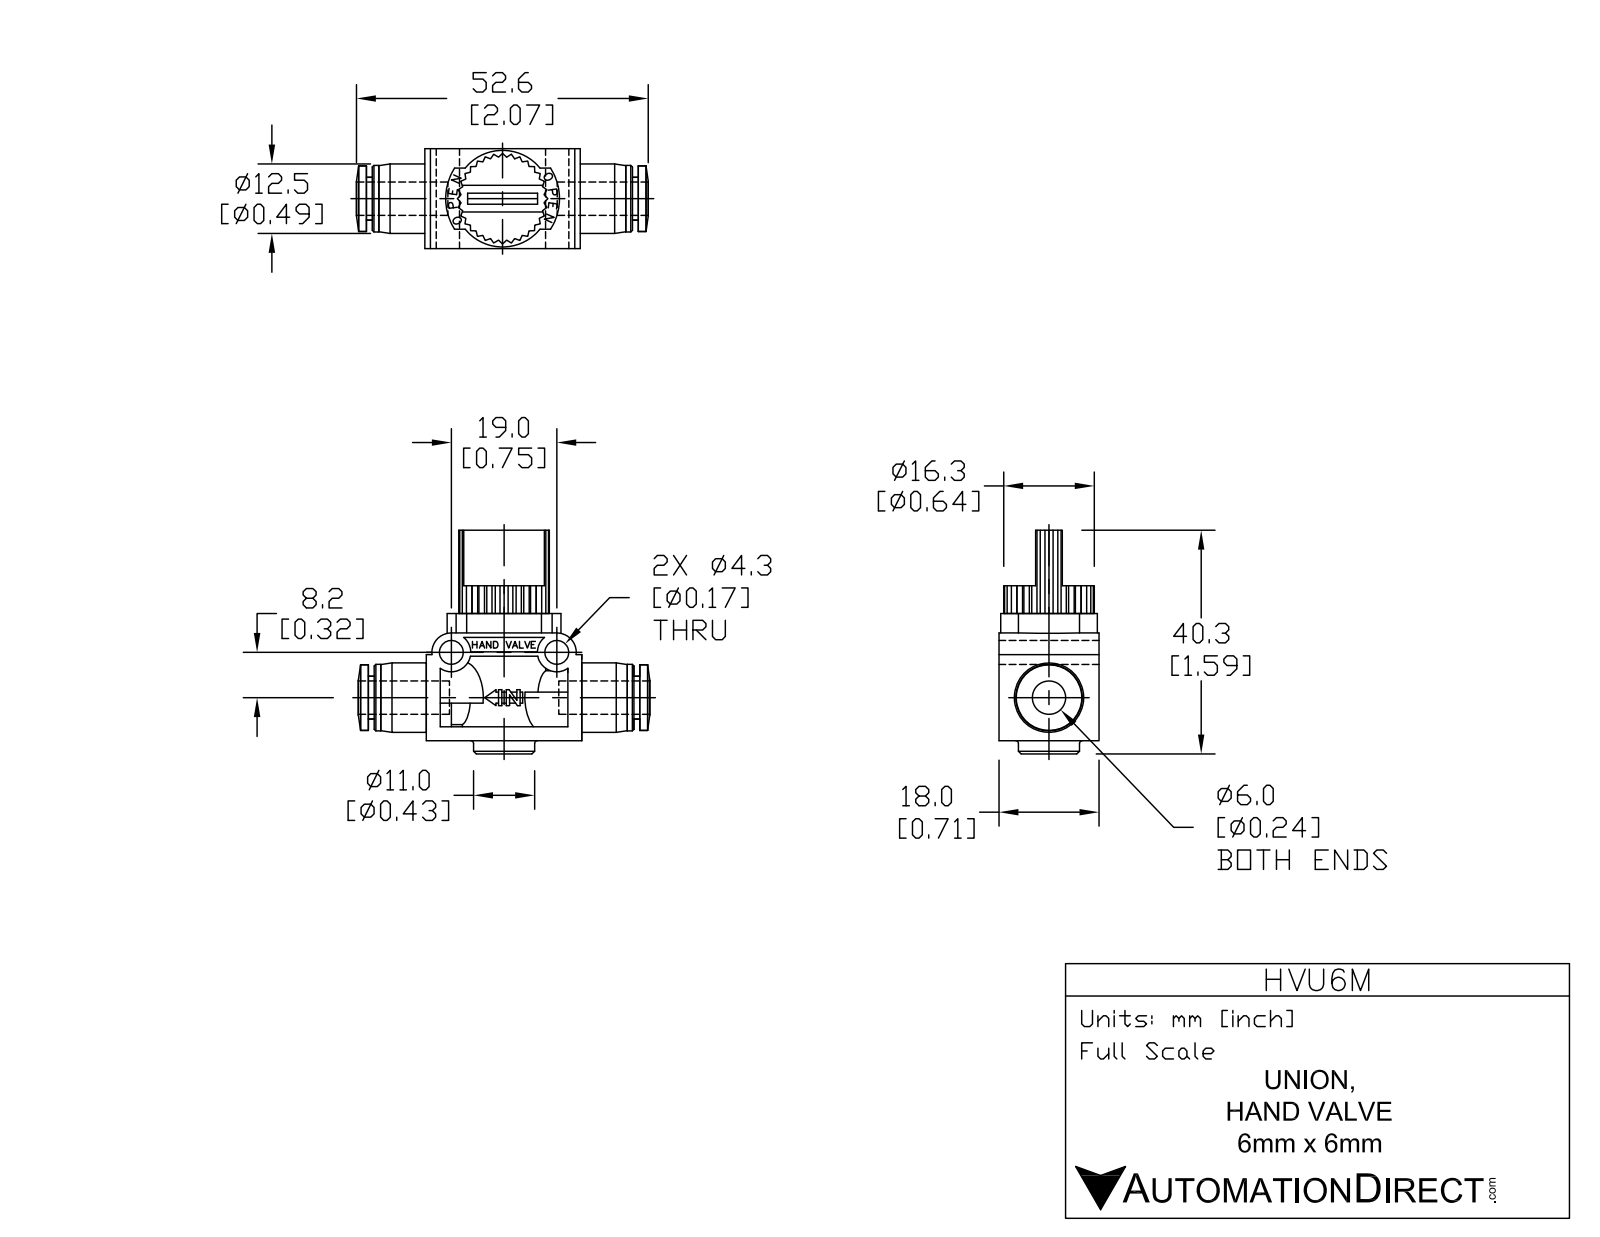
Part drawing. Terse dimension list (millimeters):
name: HVU6M
written by: SolidWorks 2015 (AUTOMOTIVE_DESIGN)
unit: mm
bodies: 1 solid, 278 faces (177 planar, 77 cylindrical, 24 other)
size: 52.5 × 40.3 × 18
volume: 11 700 mm³; area: 7 019 mm²
holes: 2× ⌀4.3, 1× ⌀6.3
bosses: 1× ⌀15, 1× ⌀12.5, 1× ⌀12, 1× ⌀11.8, 1× ⌀11, 1× ⌀7.7
rounds: 2× R3.5, 1× R4.8, 1× R5.5, 1× R6.5, 1× R7.7, 1× R7.9, 1× R8.7, 1× R10.3
face distances: 2.5, 6.6, 11.4, 3.4, 10, 8, 11.9, 1.4, 18, 2
hole spacings: 19
